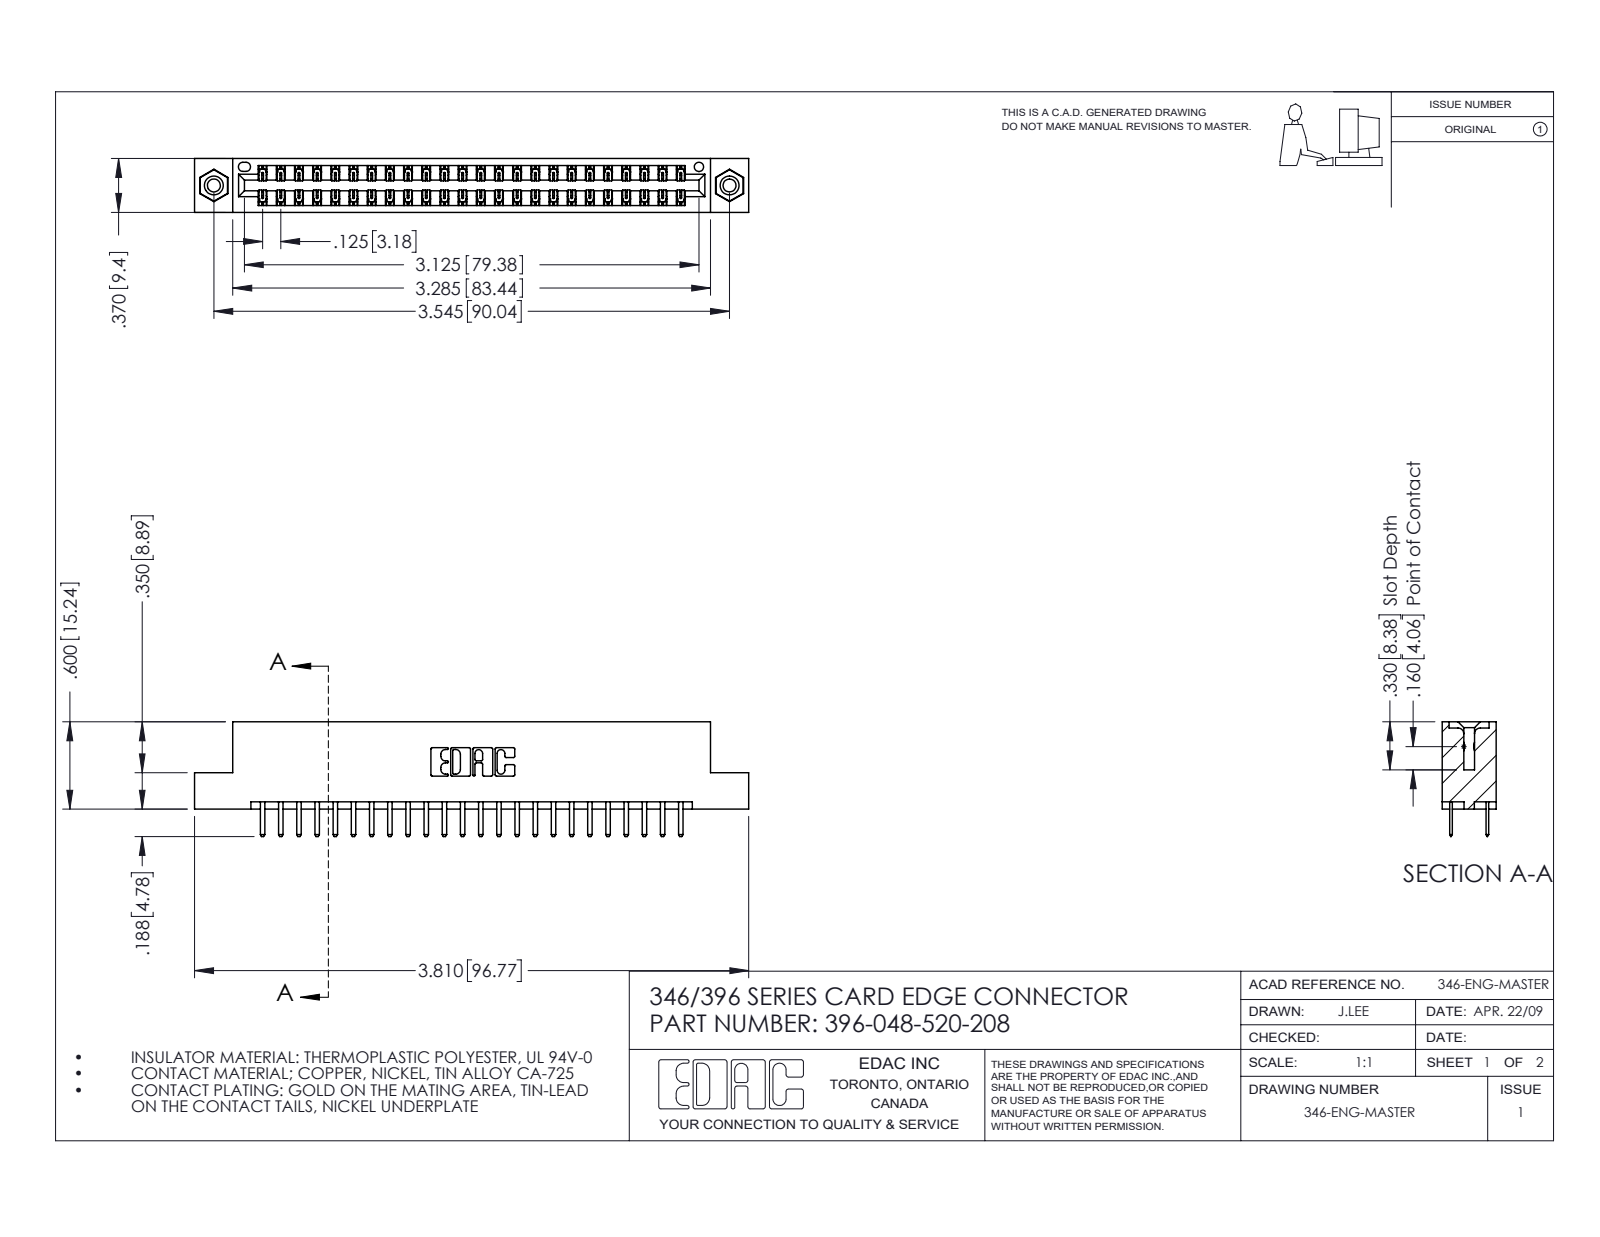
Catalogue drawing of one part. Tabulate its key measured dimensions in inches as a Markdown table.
| quantity | value |
| --- | --- |
| part name | 396-048-520-208; 345-250-001_345-250-003-102; 346 Part_Flush Mounting Lugs - 0.156 Dia-TI; 345-292-001_345-293-120 |
| STEP written by | SolidWorks 2016 (CONFIG_CONTROL_DESIGN) |
| units | inches |
| bodies | 51 solids, 2870 faces (1884 planar, 970 cylindrical, 16 other) |
| overall size | 3.81 × 0.788 × 0.37 |
| volume | 0.566 in³ |
| surface area | 19.26 in² |
| round holes (diameter × count) | 0.089 × 2, 0.125 × 2, 0.156 × 2, 0.064 × 1 |
| round bosses / shafts (diameter × count) | 0.155 × 2 |
| partial cylindrical surfaces (radius × count) | 0.006 × 72, 0.01 × 52, 0.01 × 22, 0.007 × 6, 0.031 × 6, 0.026 × 3, 0.014 × 2, 0.022 × 2 |
| main face-to-face distances | 0.048, 0.322, 0.25, 0.37, 0.275, 0.072, 0.298, 0.025, 0.148, 0.222 |
| hole center spacings | 0.246, 3.337, 3.545 |
